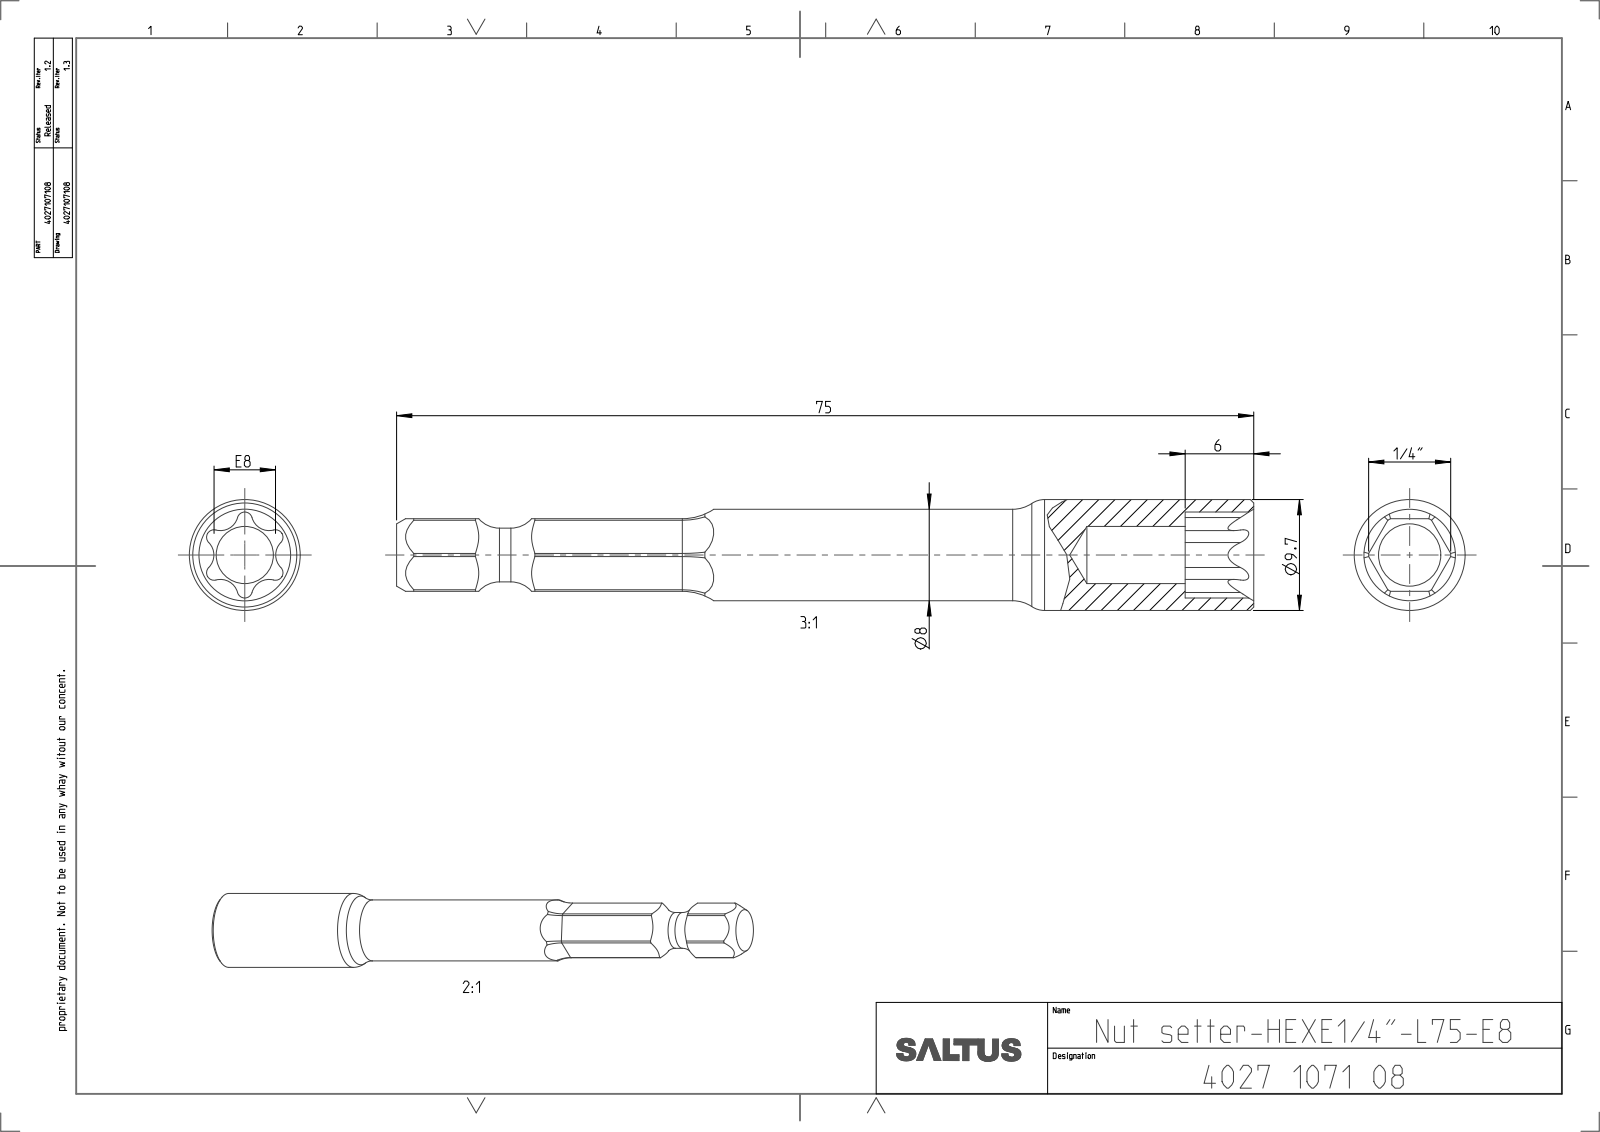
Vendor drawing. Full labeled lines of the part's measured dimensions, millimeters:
Part name (STEP PRODUCT): 4027107108
STEP written by: CREO PARAMETRIC BY PTC INC, 2022414 (CONFIG_CONTROL_DESIGN)
Units: millimetres
Bodies: 1 solid, 75 faces (15 planar, 38 cylindrical, 22 other)
Overall size (bounding box): 75 × 9.7 × 9.7
Volume: 3 361 mm³ · Surface area: 2 255 mm²
Round holes (diameter × count): ⌀5 ×1
Round bosses / shafts (diameter × count): ⌀9.7 ×1, ⌀8 ×1, ⌀4.7 ×1
Partial cylindrical surfaces — rounded edges, fillets, slot ends (radius × count): R0.66 ×6, R1.55 ×6, R5 ×6, R3.59 ×1
Main face-to-face distances: 6.34, 6.36, 75, 69, 6
